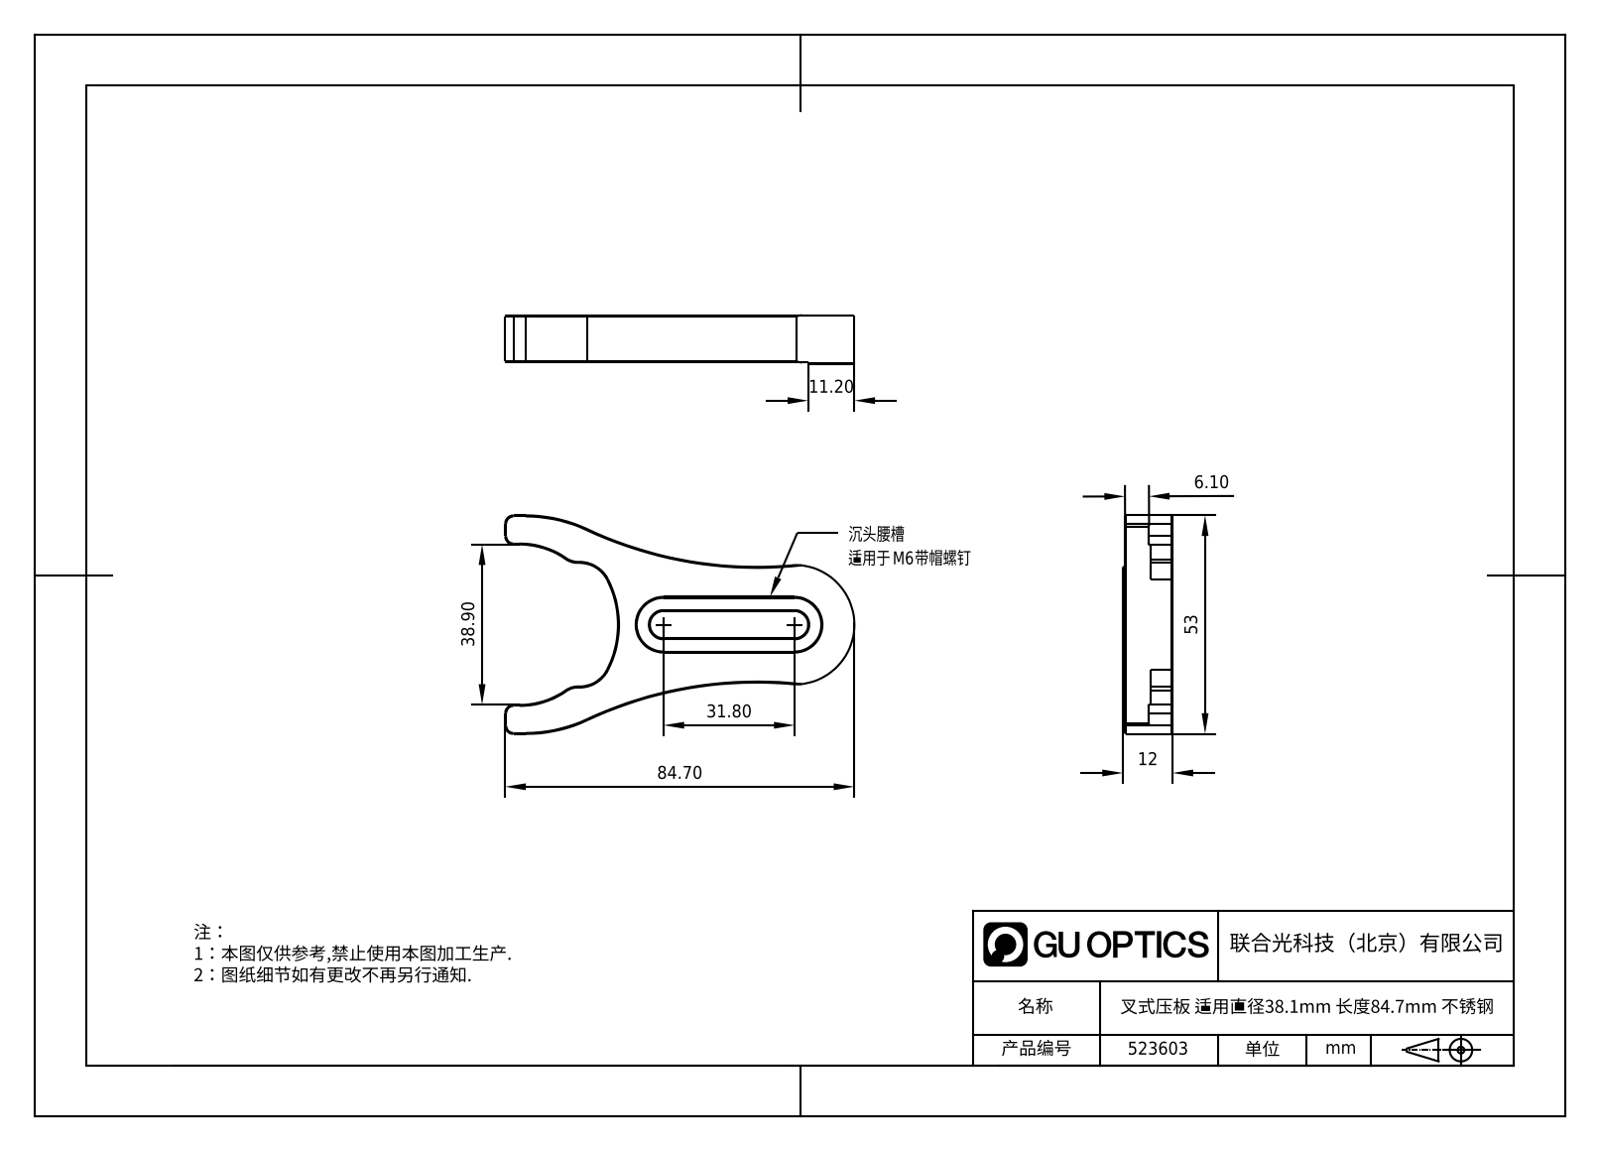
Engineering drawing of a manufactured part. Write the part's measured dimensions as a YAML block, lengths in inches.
part_name: "1.4.5.22_ZGY-1.5C_不锈钢1.5英寸光学叉型压板，C型"
step_written_by: "SolidWorks 2021 (CONFIG_CONTROL_DESIGN)"
units: inches
bodies: {solids: 1, faces: 111, planar: 44, cylindrical: 27, other: 40}
overall_size: [3.335, 2.087, 0.472]
volume: 1.151
surface_area: 12.36
partial_cylinders:
  - {radius: 0.079, count: 4}
  - {radius: 0.02, count: 2}
  - {radius: 0.13, count: 2}
  - {radius: 0.157, count: 2}
  - {radius: 0.197, count: 2}
  - {radius: 0.256, count: 2}
  - {radius: 0.295, count: 2}
  - {radius: 1.378, count: 2}
face_to_face_distances: [0.453, 0.126, 0.386, 0.26, 0.209, 0.244, 0.02, 0.228, 0.472, 0.512]
